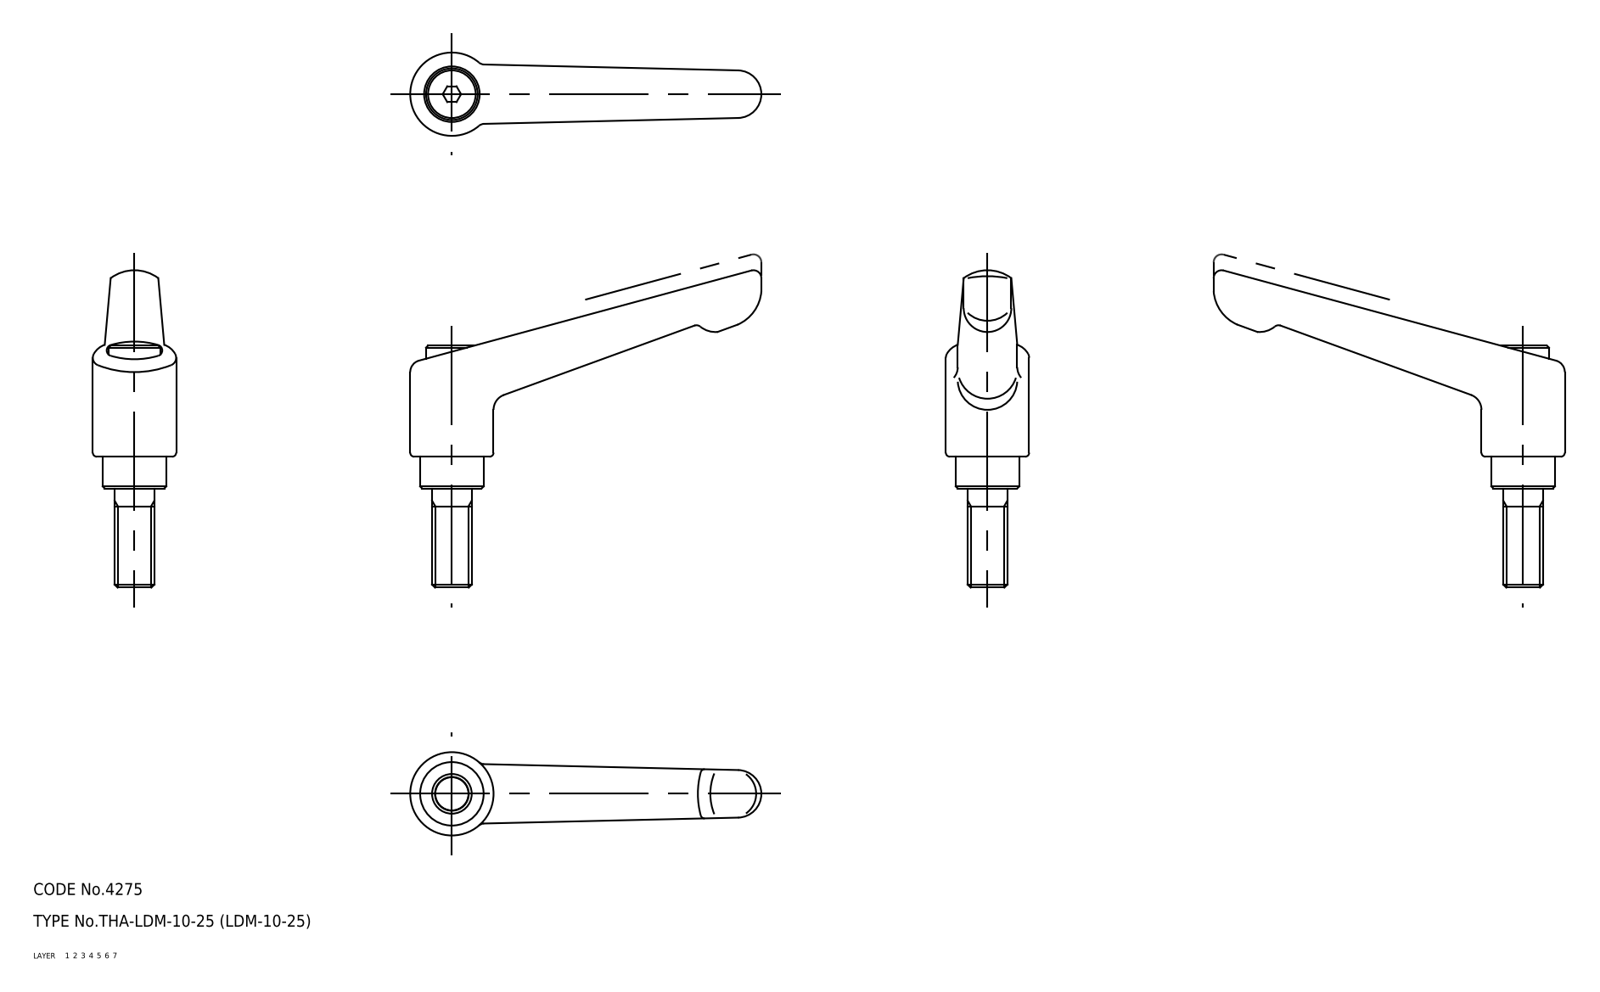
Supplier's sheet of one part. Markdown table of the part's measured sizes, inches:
| quantity | value |
| --- | --- |
| part name | sleeve; screw; handle; LDM_10_25_25963_36 |
| STEP written by | CADfix (AUTOMOTIVE_DESIGN) |
| units | inches |
| bodies | 3 solids, 75 faces (0 planar, 0 cylindrical, 75 other) |
| overall size | 3.484 × 3.15 × 0.827 |
| volume | 1.301 in³ |
| surface area | 14.13 in² |
